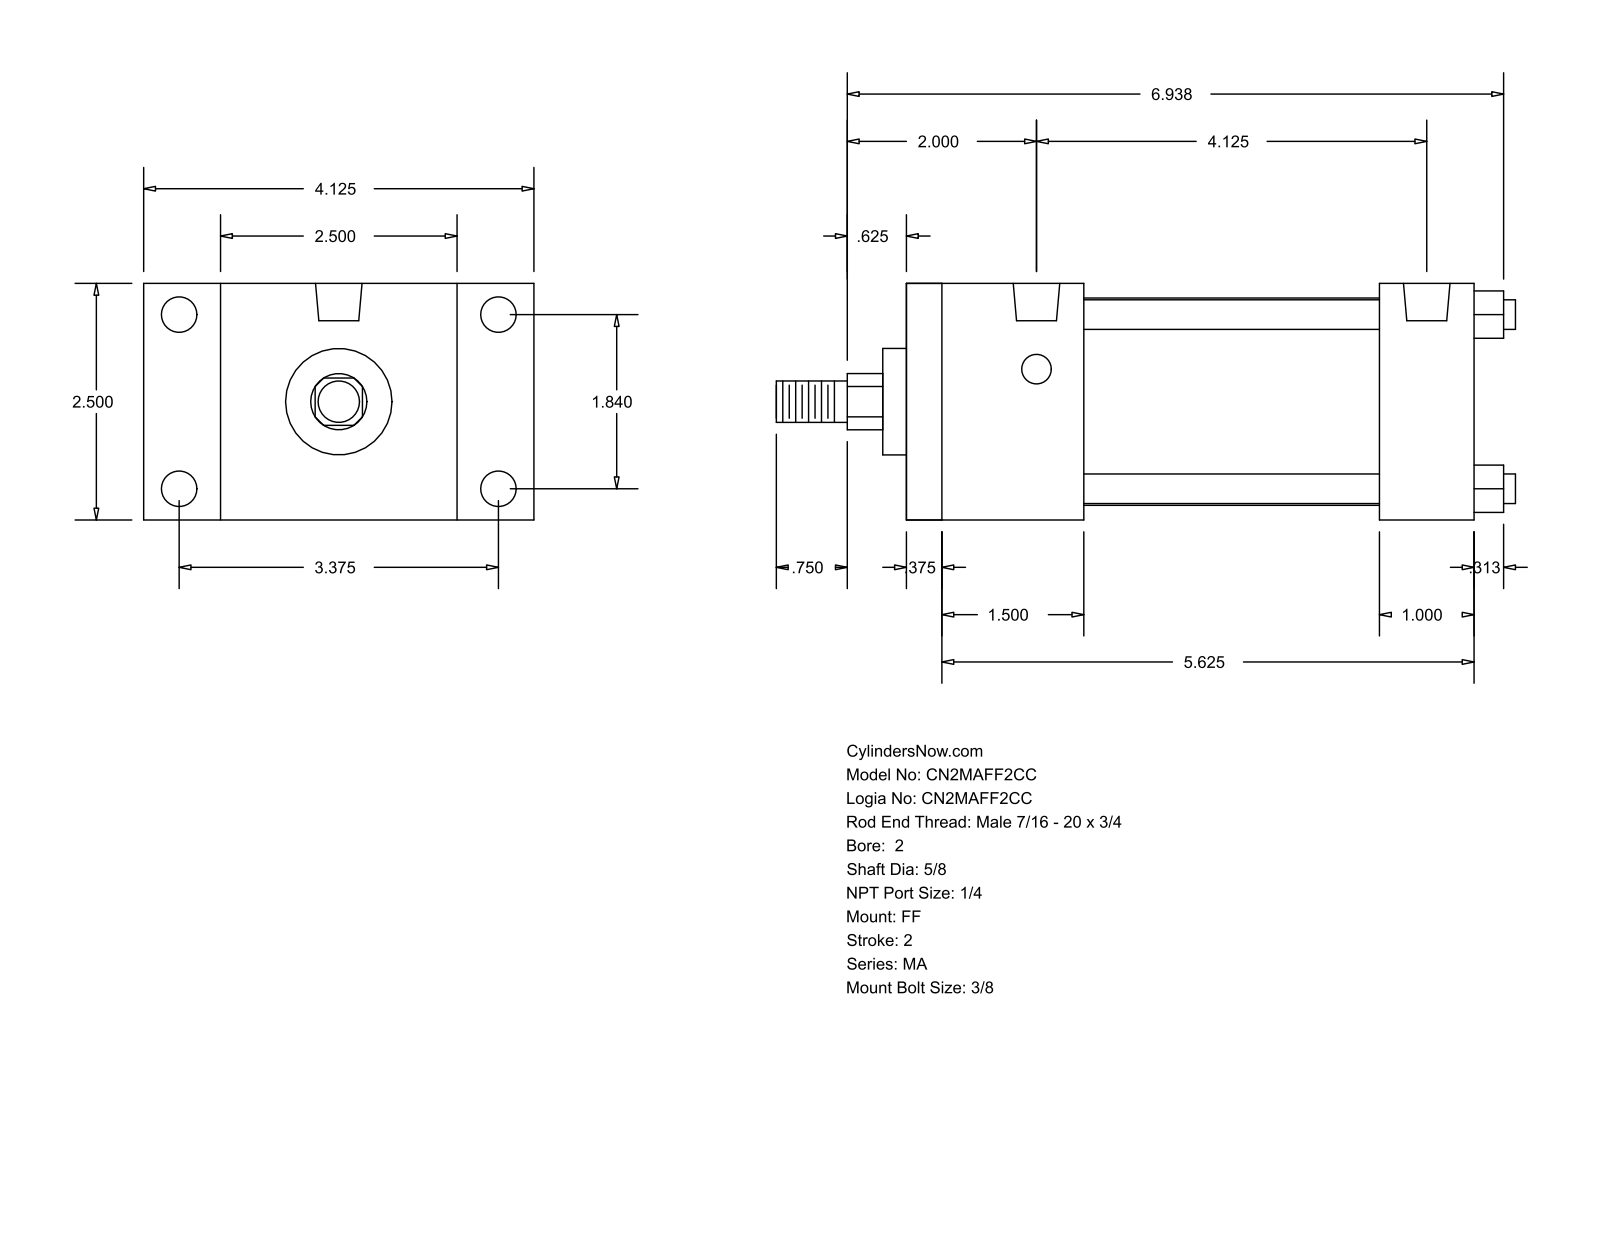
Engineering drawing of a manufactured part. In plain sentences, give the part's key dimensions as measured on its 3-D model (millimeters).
The part is named "MA_FF__0200_0.625". Its 3-D file was written by "GSSL Pune (CONFIG_CONTROL_DESIGN)". It is 0 solids with 92 faces: 64 planar, 28 cylindrical and 0 other. Overall it measures 198.44 by 104.78 by 63.5 millimeters. Round holes: 4 of diameter 7.94, 4 of diameter 9.53, 2 of diameter 12.49. Round bosses or shafts: 4 of diameter 7.94, 1 of diameter 55.63, 1 of diameter 28.57, 1 of diameter 15.88, 1 of diameter 11.11. Partial cylindrical surfaces (rounded edges, fillets, slot ends): 1 of radius 7.54. The main face-to-face distances are 63.5, 152.4, 142.88, 9.52, 104.78, 25.4, 38.1, 47.62, 127, 117.48. The hole center spacings are 46.74, 85.72, 97.63, 104.77.
